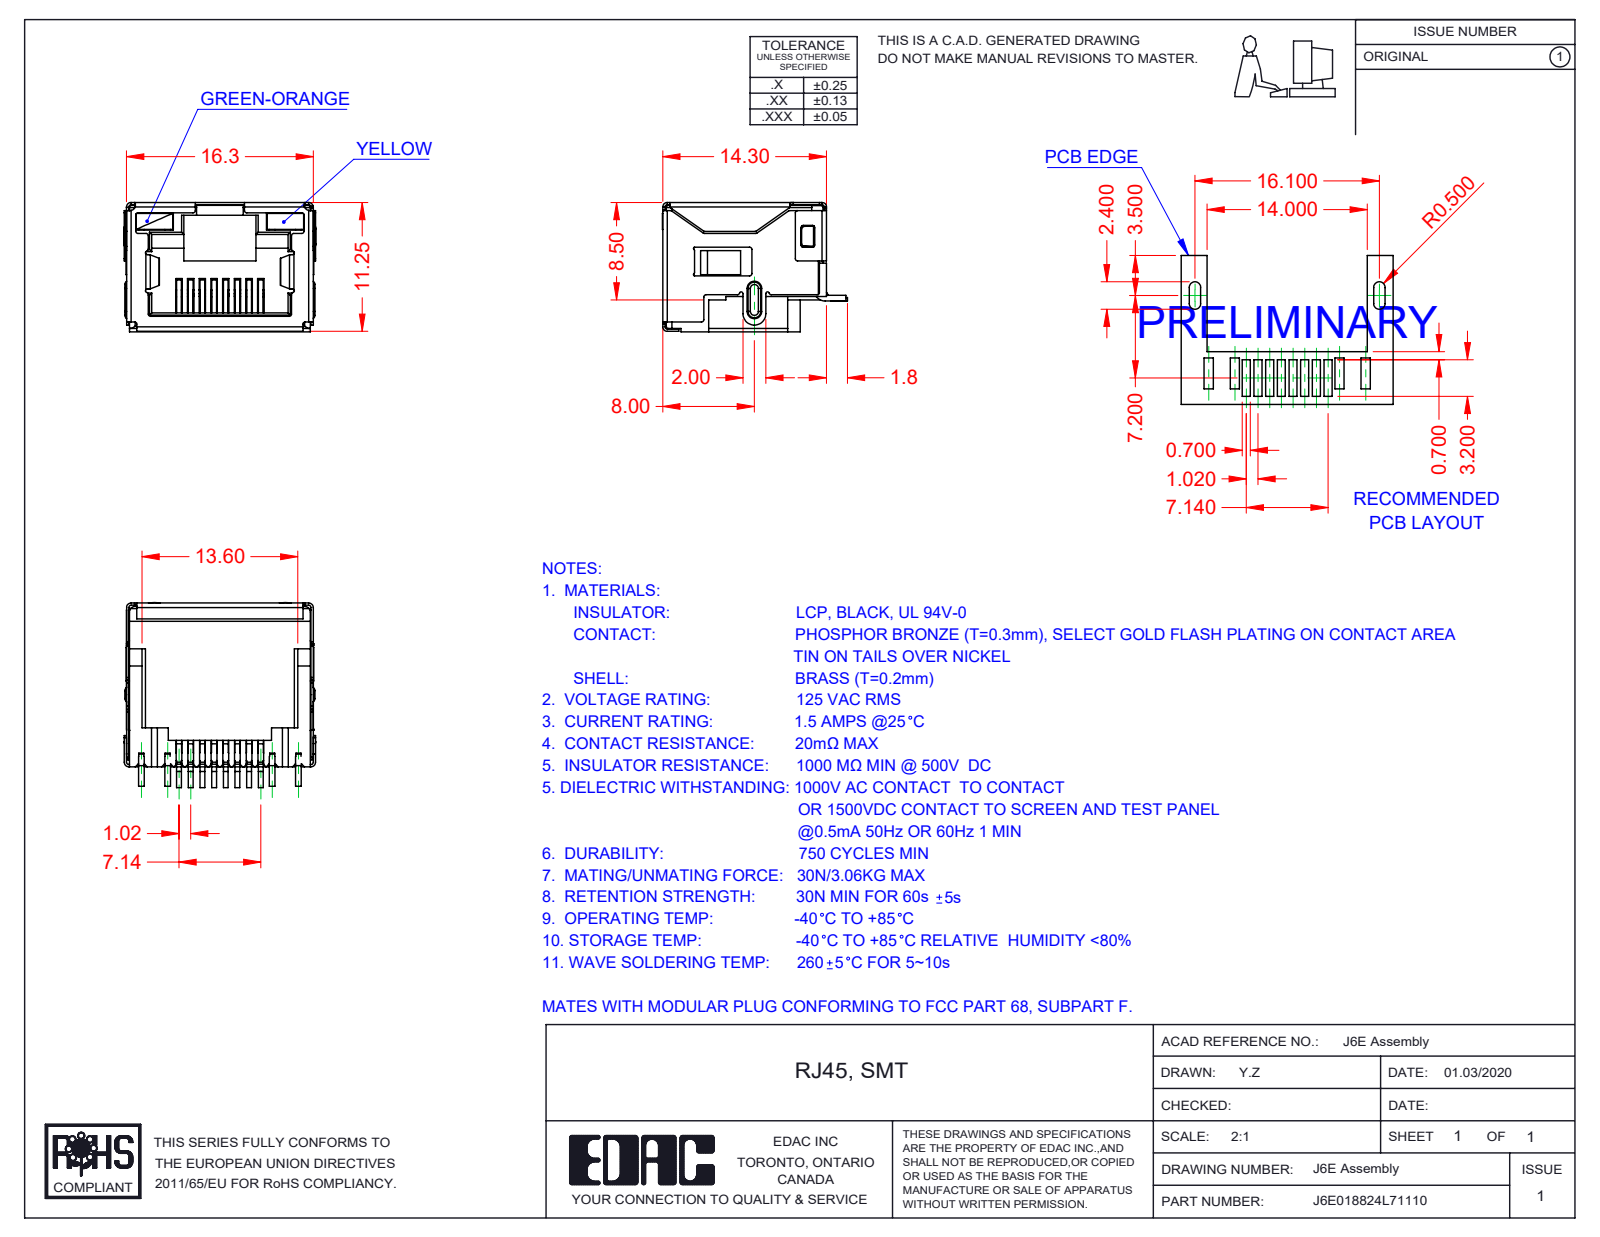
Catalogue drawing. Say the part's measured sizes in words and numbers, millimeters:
The part is named "J6E018824L71110; 6E LED RH_1-Yellow; 6E LED LH_7-Green-Orange; 6E Shield_LED (+2 more)". Its 3-D file was written by "SolidWorks 2016 (CONFIG_CONTROL_DESIGN)". It is 12 solids with 1498 faces: 1099 planar, 349 cylindrical and 50 other. Overall it measures 16.75 by 16.15 by 11.3 millimeters. Its volume is 1 109 cubic millimeters and its surface area 4 045 square millimeters. Partial cylindrical surfaces (rounded edges, fillets, slot ends): 82 of radius 0.2, 17 of radius 0.25, 13 of radius 0.4, 13 of radius 0.5, 10 of radius 0.1, 7 of radius 0.15, 4 of radius 0.3, 3 of radius 1. The main face-to-face distances are 11.05, 16.05, 16.1, 15.85, 11.1, 11.3, 2.4, 0.7, 9.85, 0.49.
